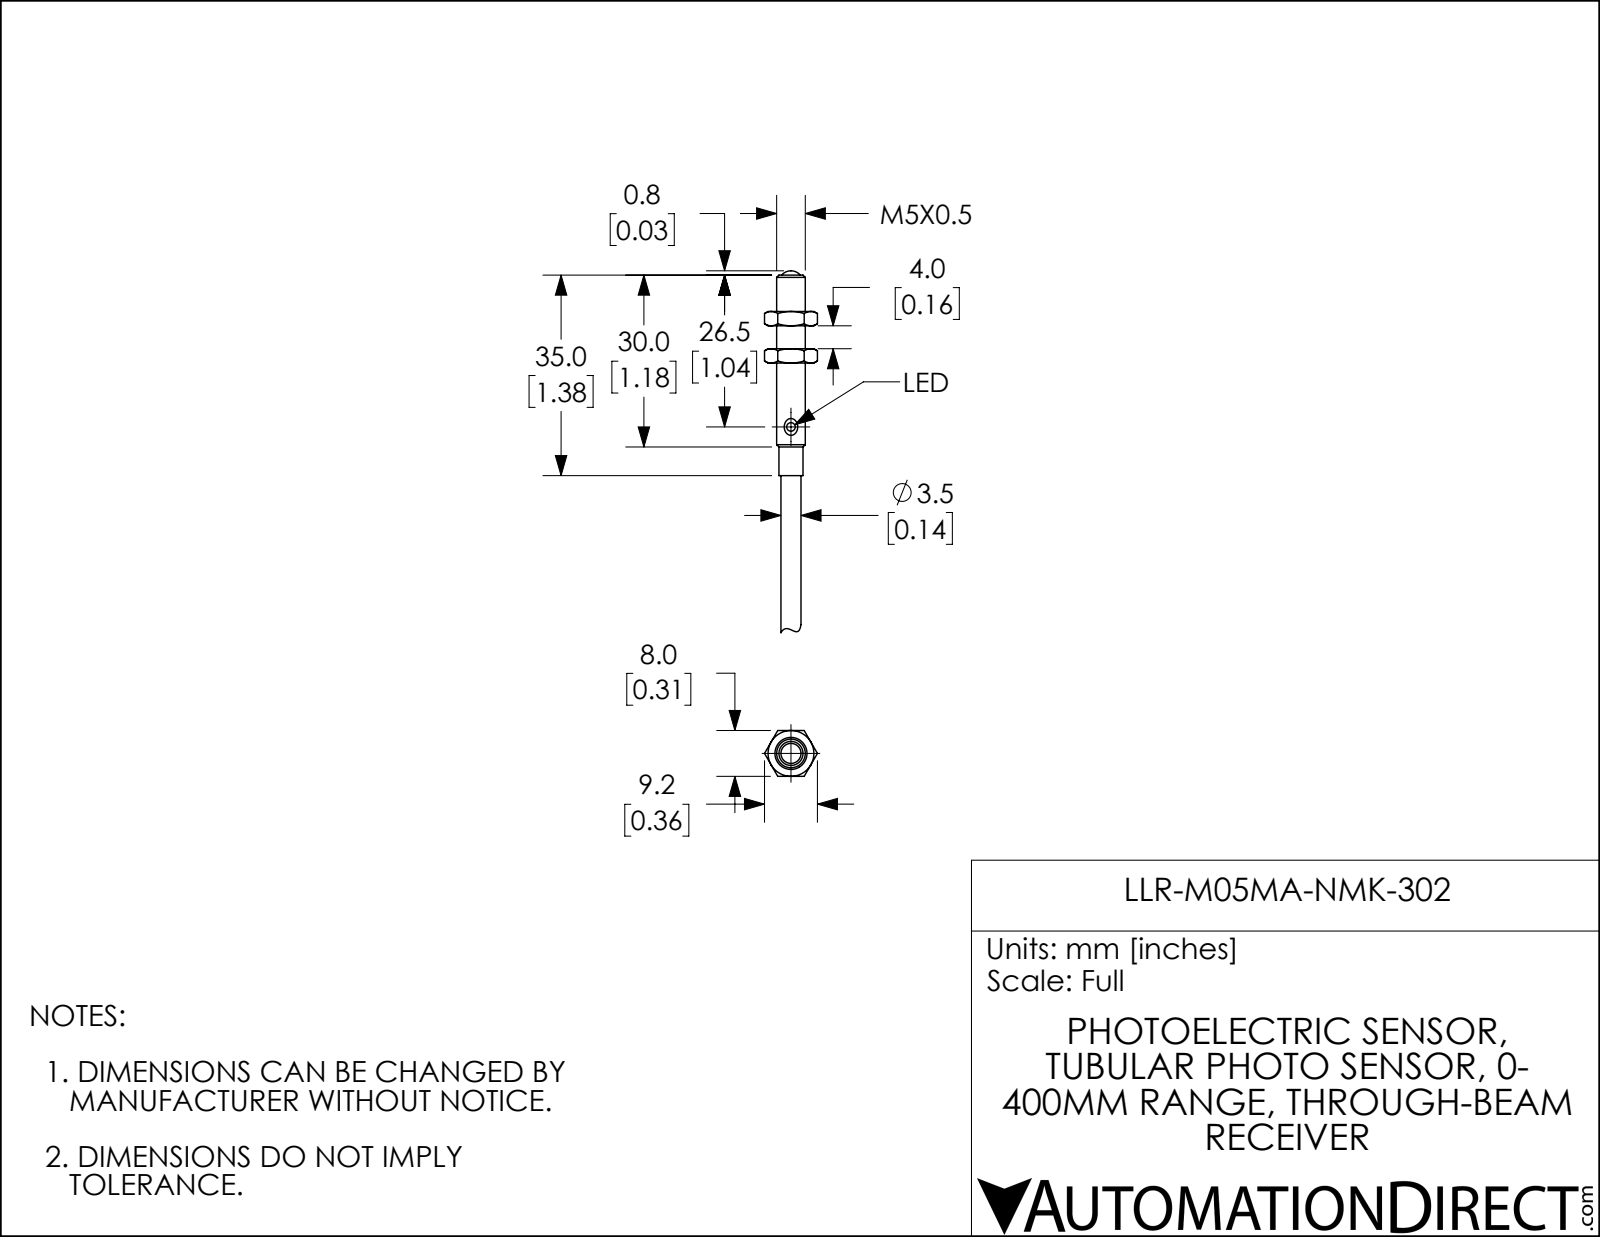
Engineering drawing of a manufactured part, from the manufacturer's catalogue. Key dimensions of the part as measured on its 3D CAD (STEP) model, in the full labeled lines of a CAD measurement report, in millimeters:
Part name (STEP PRODUCT): LLR-M05MA-NMK-302
STEP written by: SolidWorks 2018 (AUTOMOTIVE_DESIGN)
Units: millimetres
Bodies: 4 solids, 65 faces (21 planar, 10 cylindrical, 34 other)
Overall size (bounding box): 63.2 × 9.2 × 8
Volume: 1 200 mm³ · Surface area: 1 366 mm²
Round holes (diameter × count): ⌀1.5 ×1, ⌀5 ×1
Round bosses / shafts (diameter × count): ⌀4.2 ×1, ⌀3.6 ×1, ⌀3.5 ×1
Main face-to-face distances: 8, 6.5, 2.5, 9, 4, 3.7, 1.1, 2.8, 5.4, 15.3
